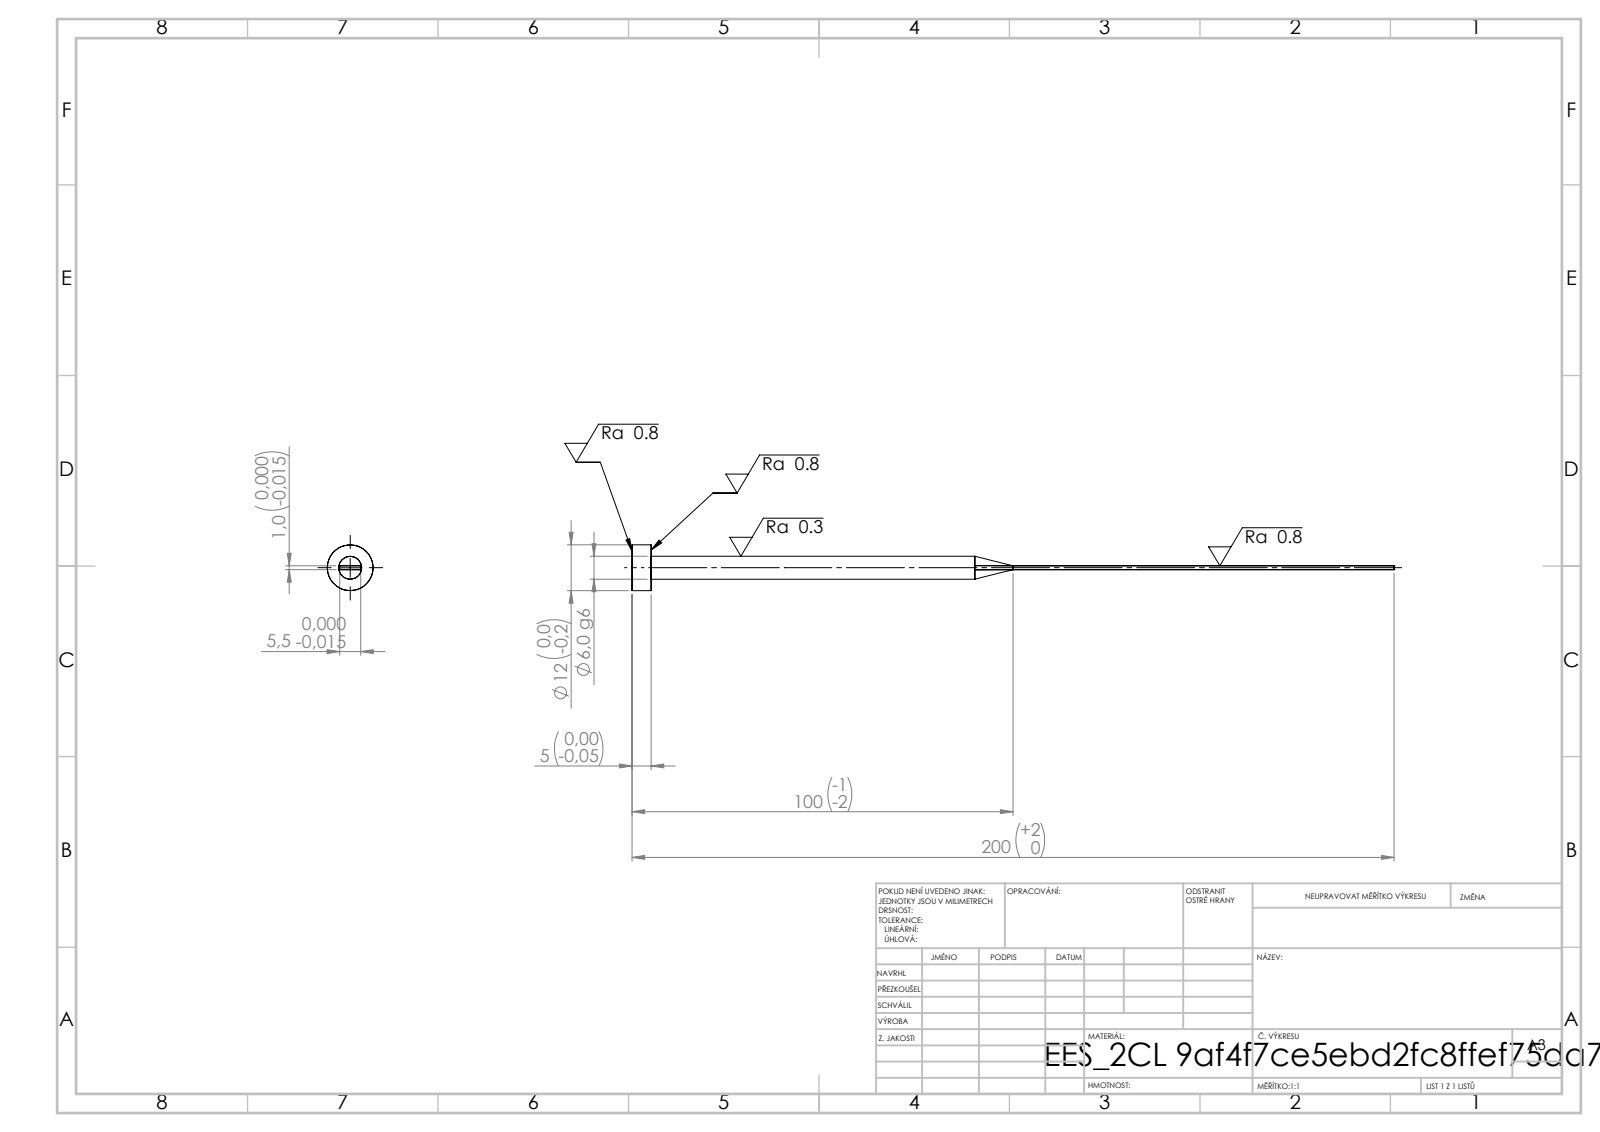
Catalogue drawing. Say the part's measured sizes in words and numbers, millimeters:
Its 3-D file was written by "SolidWorks 2019 (CONFIG_CONTROL_DESIGN)". It is 1 solid with 15 faces: 7 planar, 4 cylindrical and 4 other. Overall it measures 200 by 12 by 12 millimeters. Its volume is 3 678 cubic millimeters and its surface area 3 448 square millimeters. Round bosses or shafts: 1 of diameter 12, 1 of diameter 6. The main face-to-face distances are 1, 5.5, 5, 200, 195.
